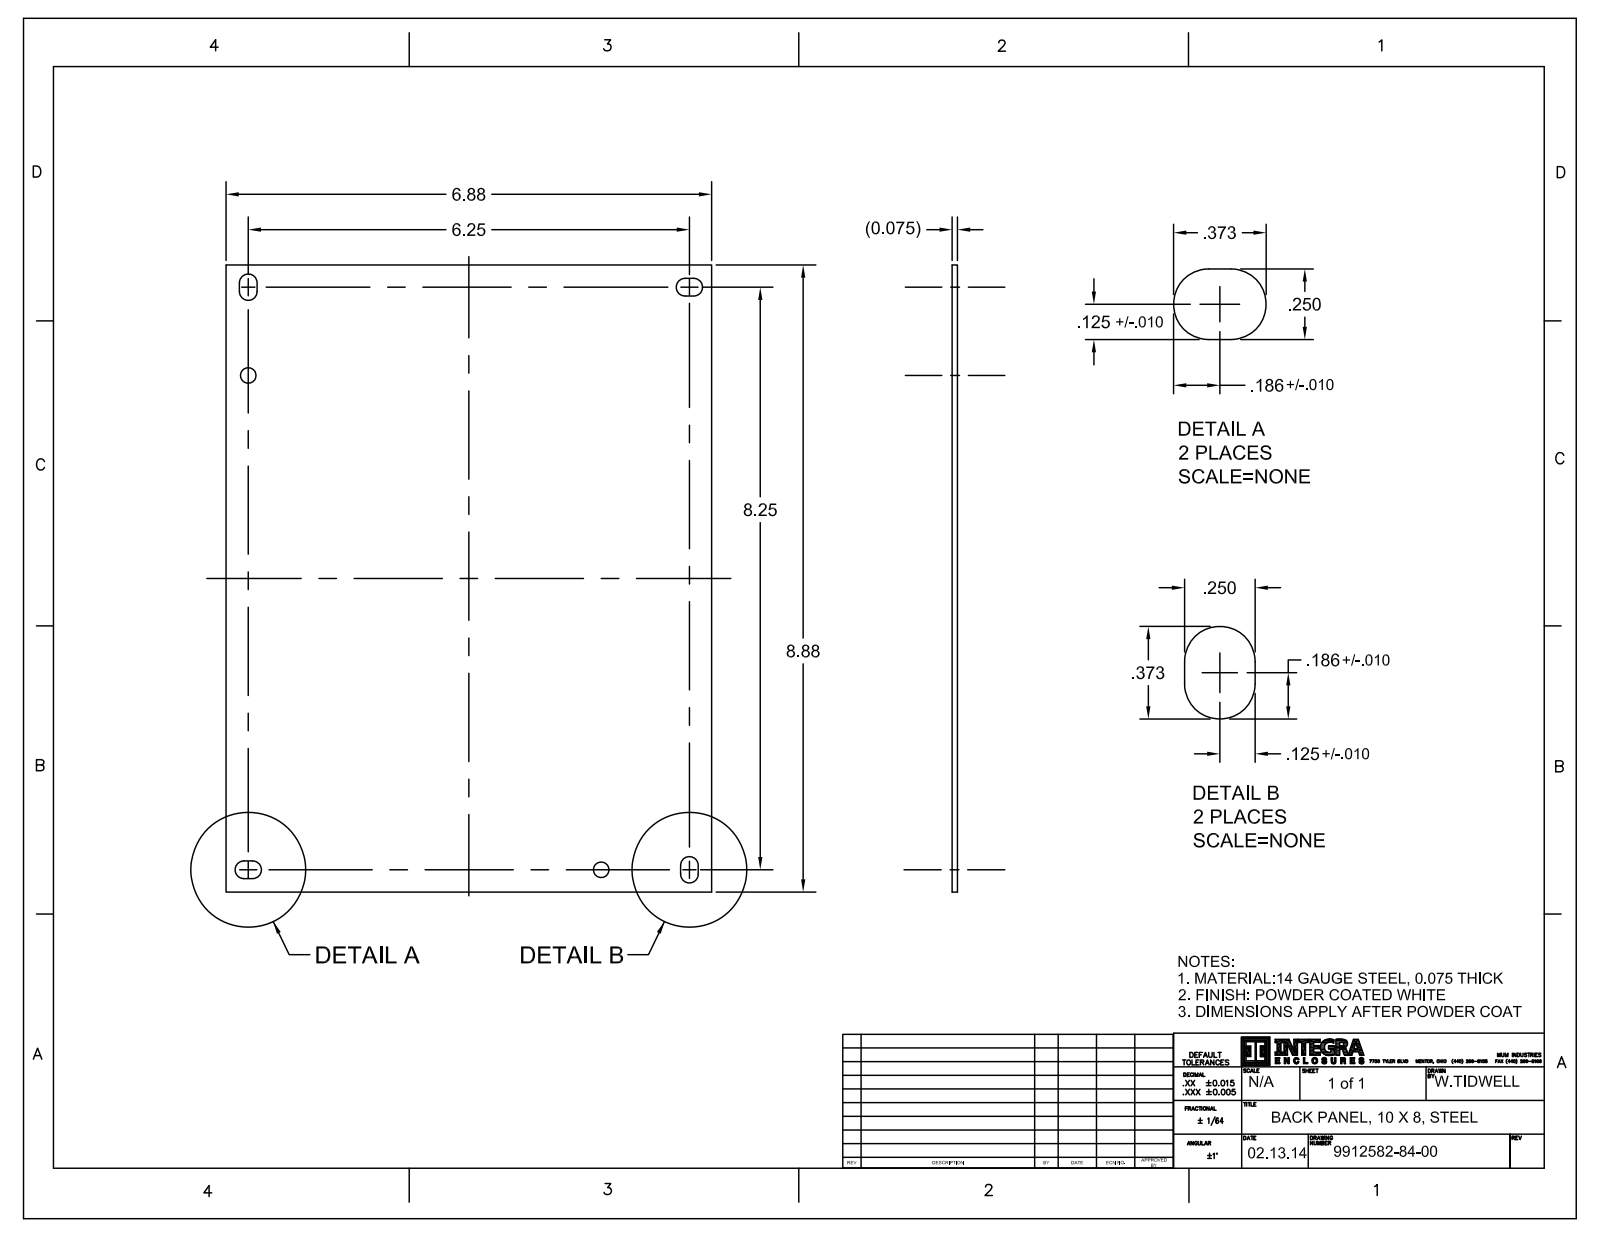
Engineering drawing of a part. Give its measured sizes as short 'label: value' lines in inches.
name: 9912582-84-00; 9912594-82-10; SBP108-IMP_ASM
written by: CREO PARAMETRIC BY PTC INC, 2016050 (CONFIG_CONTROL_DESIGN)
unit: in
bodies: 5 solids, 386 faces (122 planar, 156 cylindrical, 108 other)
size: 8.88 × 6.88 × 0.508
volume: 4.612 in³; area: 126.9 in²
holes: 2× ⌀0.219
bosses: 4× ⌀0.373, 4× ⌀0.19, 4× ⌀0.136
rounds: 8× R0.125
face distances: 0.075, 6.88, 8.88, 0.208, 0.133, 0.132, 0.057, 0.076, 0.25, 0.3
hole spacings: 8.602
